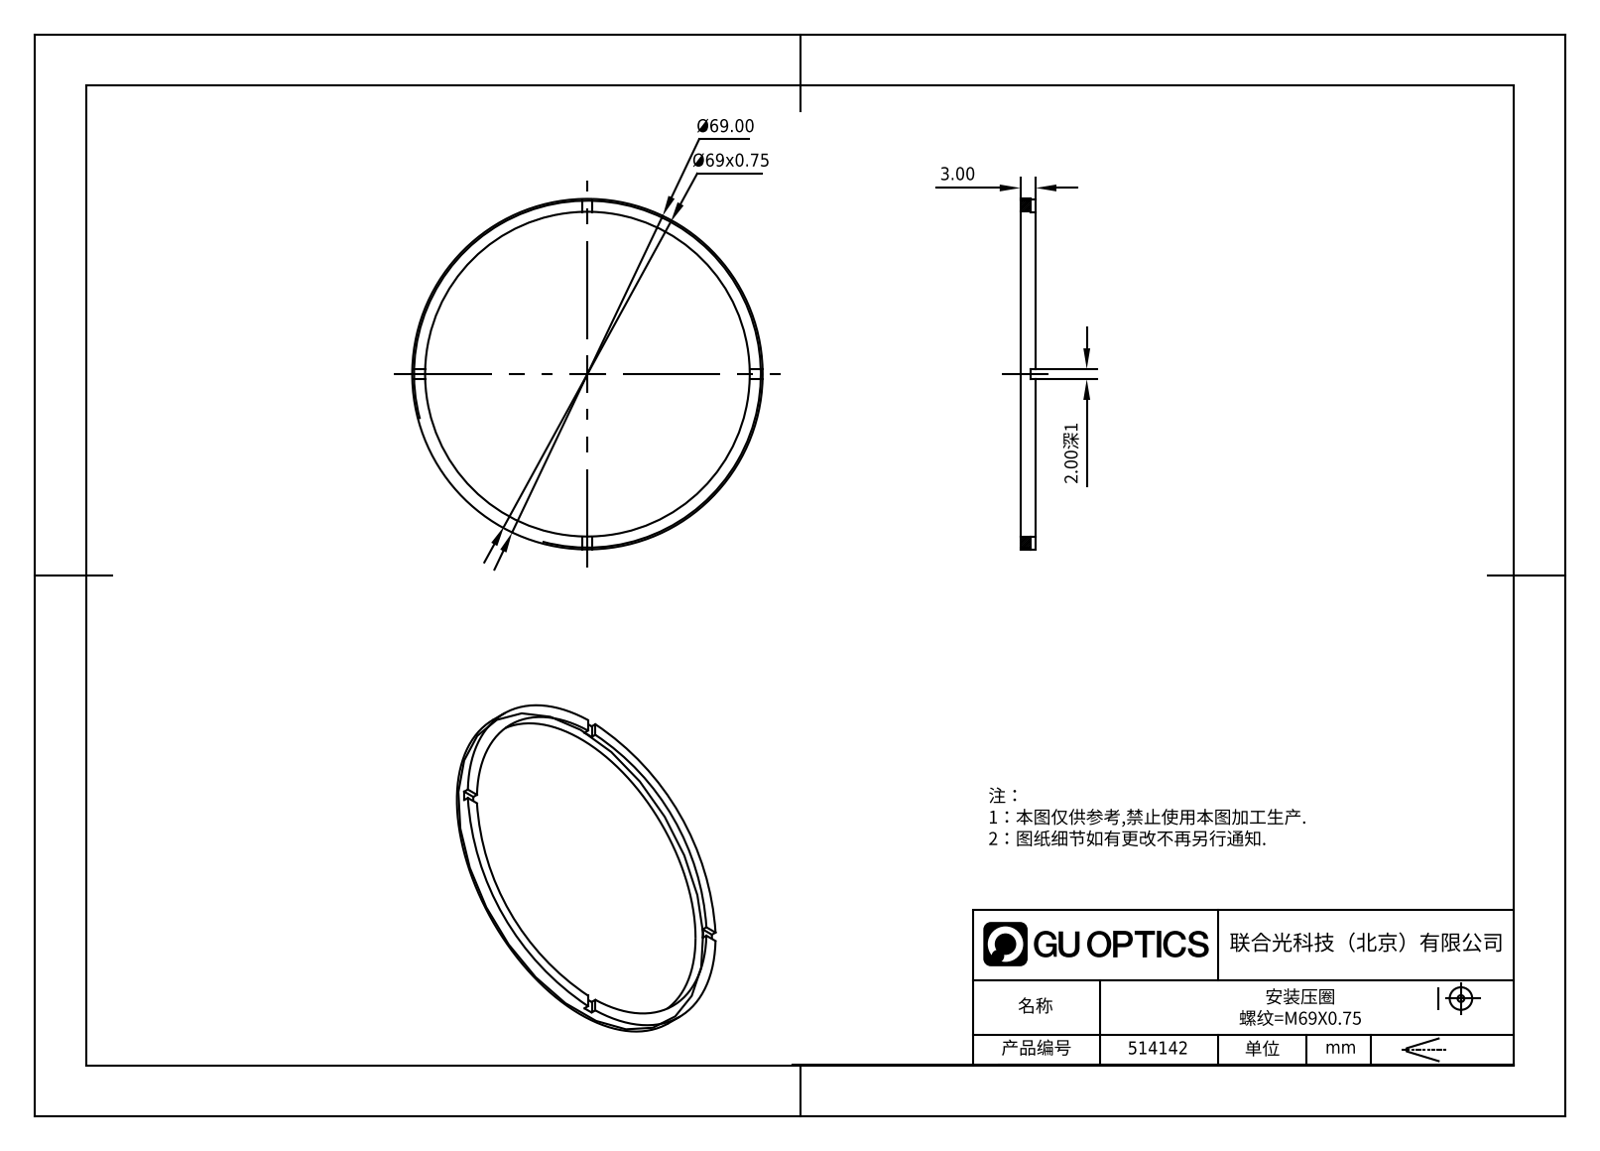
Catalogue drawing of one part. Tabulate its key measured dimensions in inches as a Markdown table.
| quantity | value |
| --- | --- |
| part name | 514142 |
| STEP written by | SolidWorks 2020 (CONFIG_CONTROL_DESIGN) |
| units | inches |
| bodies | 1 solid, 21 faces (17 planar, 4 cylindrical, 0 other) |
| overall size | 2.717 × 2.717 × 0.118 |
| volume | 0.094 in³ |
| surface area | 3.568 in² |
| round holes (diameter × count) | 2.52 × 1 |
| round bosses / shafts (diameter × count) | 2.717 × 1 |
| main face-to-face distances | 0.118, 0.079, 0.039 |
